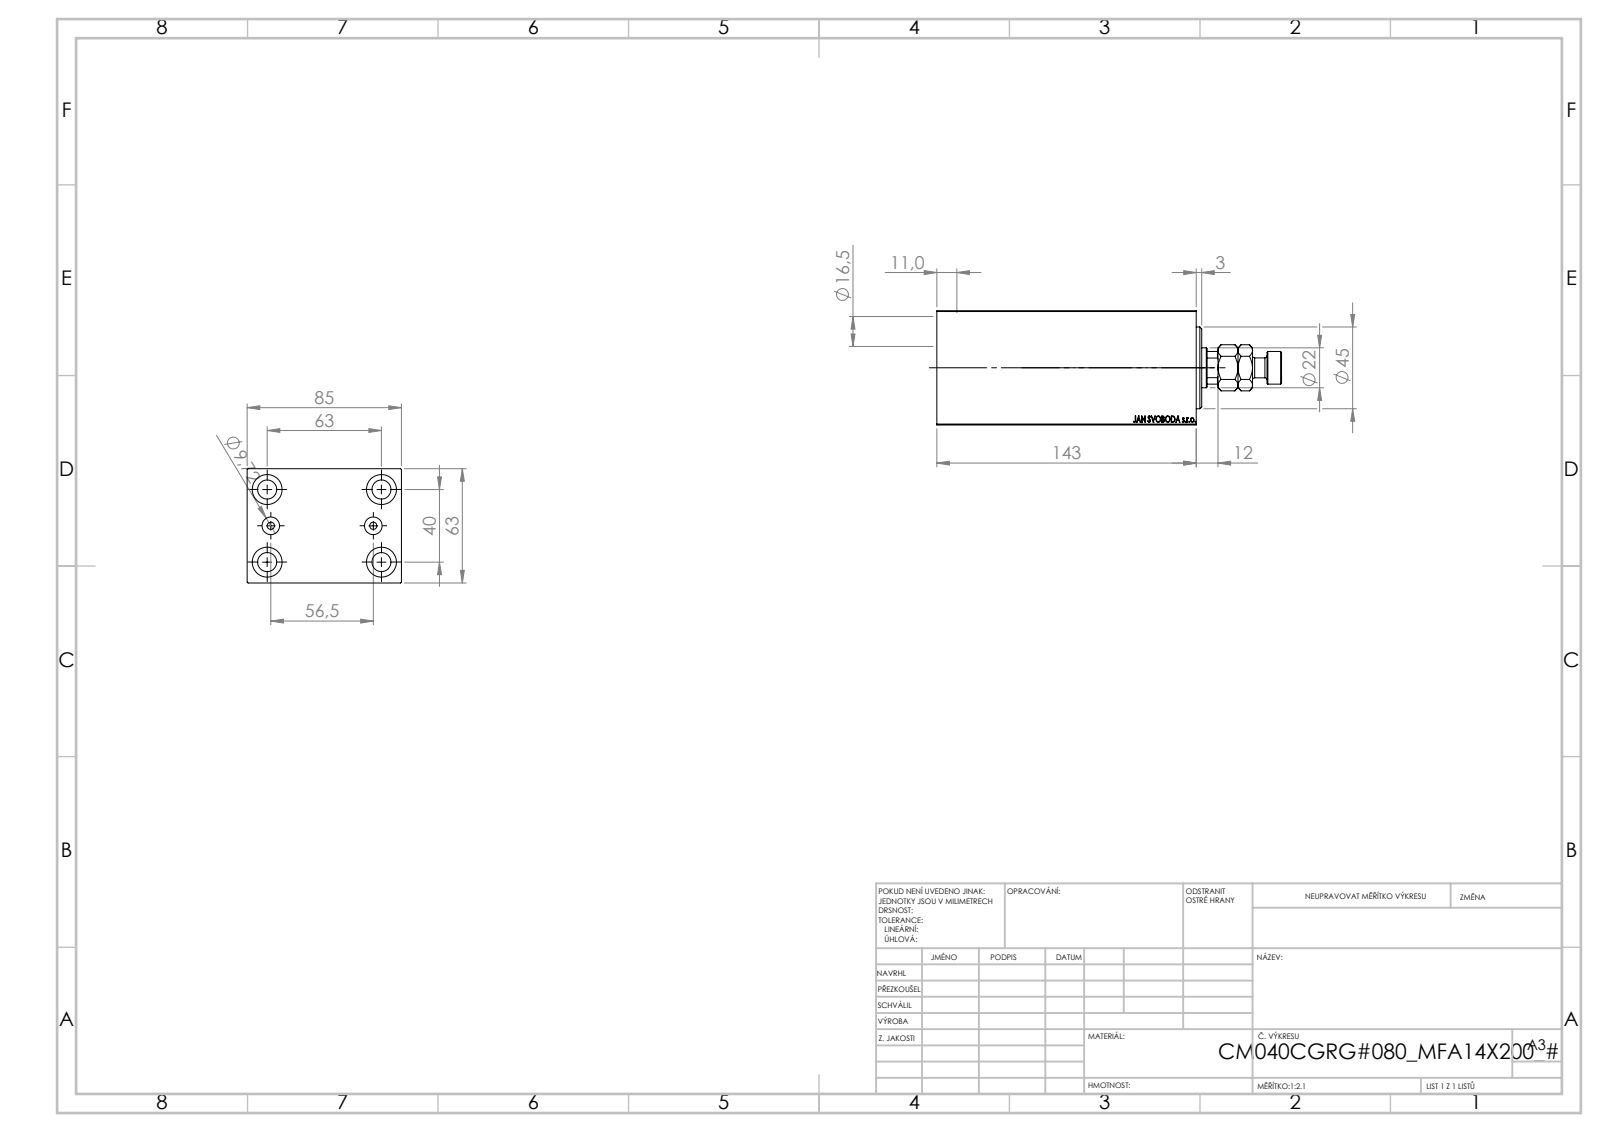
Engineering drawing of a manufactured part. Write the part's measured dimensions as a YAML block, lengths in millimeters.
part_name: "MFA; V450CM_C_VCP; V450CM_C_Body; V450CM_VC_B"
step_written_by: "SolidWorks 2019 (CONFIG_CONTROL_DESIGN)"
units: millimeters
bodies: {solids: 4, faces: 910, planar: 424, cylindrical: 60, other: 426}
overall_size: [190, 85, 63]
volume: 645705
surface_area: 117166
round_holes:
  - {diameter: 10.5, count: 4}
  - {diameter: 16.5, count: 4}
  - {diameter: 4, count: 2}
  - {diameter: 9.72, count: 2}
  - {diameter: 12.5, count: 1}
  - {diameter: 22, count: 1}
  - {diameter: 25.5, count: 1}
  - {diameter: 40, count: 1}
  - {diameter: 42, count: 1}
  - {diameter: 45, count: 1}
round_bosses_or_shafts:
  - {diameter: 18, count: 1}
  - {diameter: 11, count: 1}
partial_cylinders:
  - {radius: 10.5, count: 1}
face_to_face_distances: [63, 85, 12, 131, 143, 1, 119, 11, 132, 120]
hole_center_spacings: [37.31, 20.1, 20.5, 40, 61.82, 63, 64.2, 74.63]
